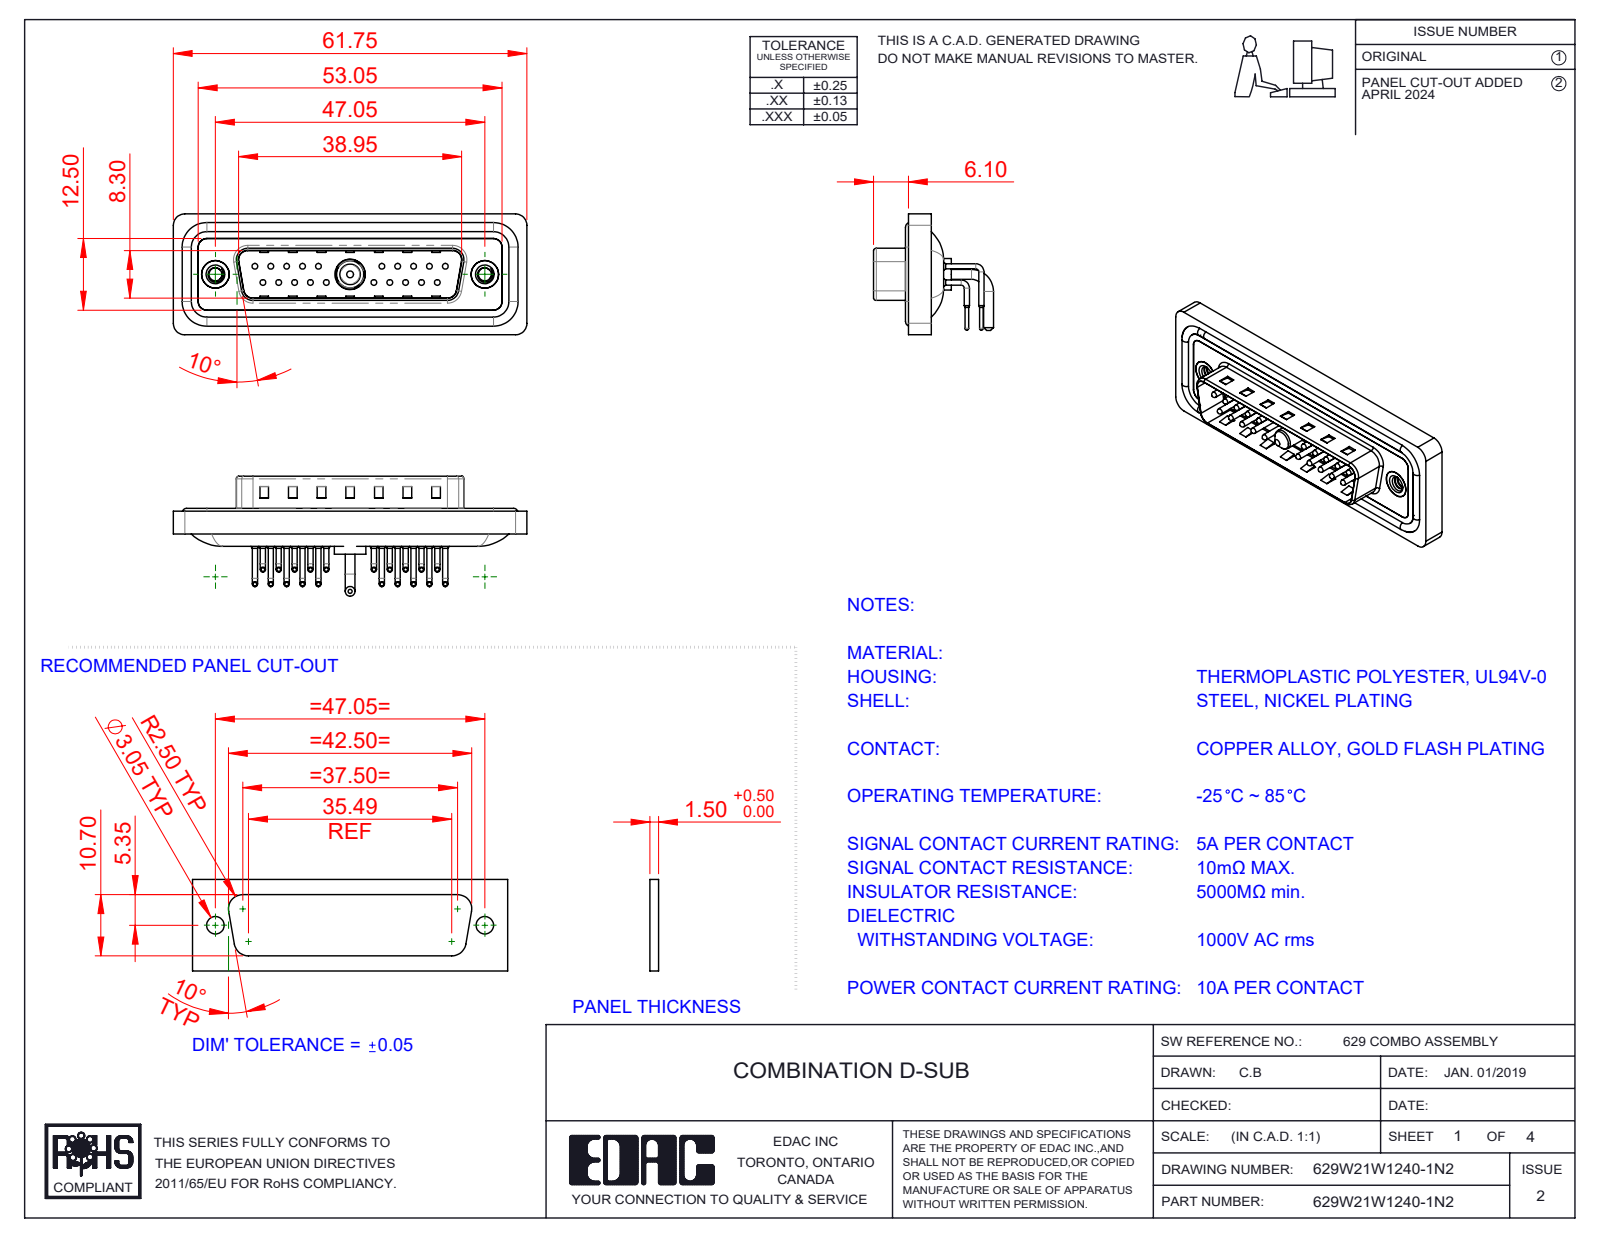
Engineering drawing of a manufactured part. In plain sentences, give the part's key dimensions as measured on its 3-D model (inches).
The part is named "Power Pin_10A RA; 629Combo Contact Row 2; 629Combo Contact Row 1; 629Combo Housing_21W1 (+5 more)". Its 3-D file was written by "SolidWorks 2023 (CONFIG_CONTROL_DESIGN)". It is 29 solids with 2726 faces: 1499 planar, 929 cylindrical and 298 other. Overall it measures 2.431 by 0.831 by 0.825 inches. Its volume is 0.45 cubic inches and its surface area 19.64 square inches. Round holes: 20 of diameter 0.03, 20 of diameter 0.063, 20 of diameter 0.079, 2 of diameter 0.089, 2 of diameter 0.157, 2 of diameter 0.189, 2 of diameter 0.197, 1 of diameter 0.191, 1 of diameter 0.209. Round bosses or shafts: 40 of diameter 0.035, 20 of diameter 0.059, 20 of diameter 0.039, 20 of diameter 0.026, 4 of diameter 0.063, 2 of diameter 0.193, 2 of diameter 0.067, 1 of diameter 0.217. Partial cylindrical surfaces (rounded edges, fillets, slot ends): 20 of radius 0.04, 18 of radius 0.059, 18 of radius 0.079, 8 of radius 0.02, 8 of radius 0.063, 4 of radius 0.01, 4 of radius 0.024, 4 of radius 0.026. The main face-to-face distances are 0.016, 0.114, 0.031, 0.161, 0.043, 0.083, 0.063, 0.177, 0.059, 0.098. The hole center spacings are 0.124, 0.109, 0.218, 0.327, 0.198, 0.763, 0.826, 0.872.
